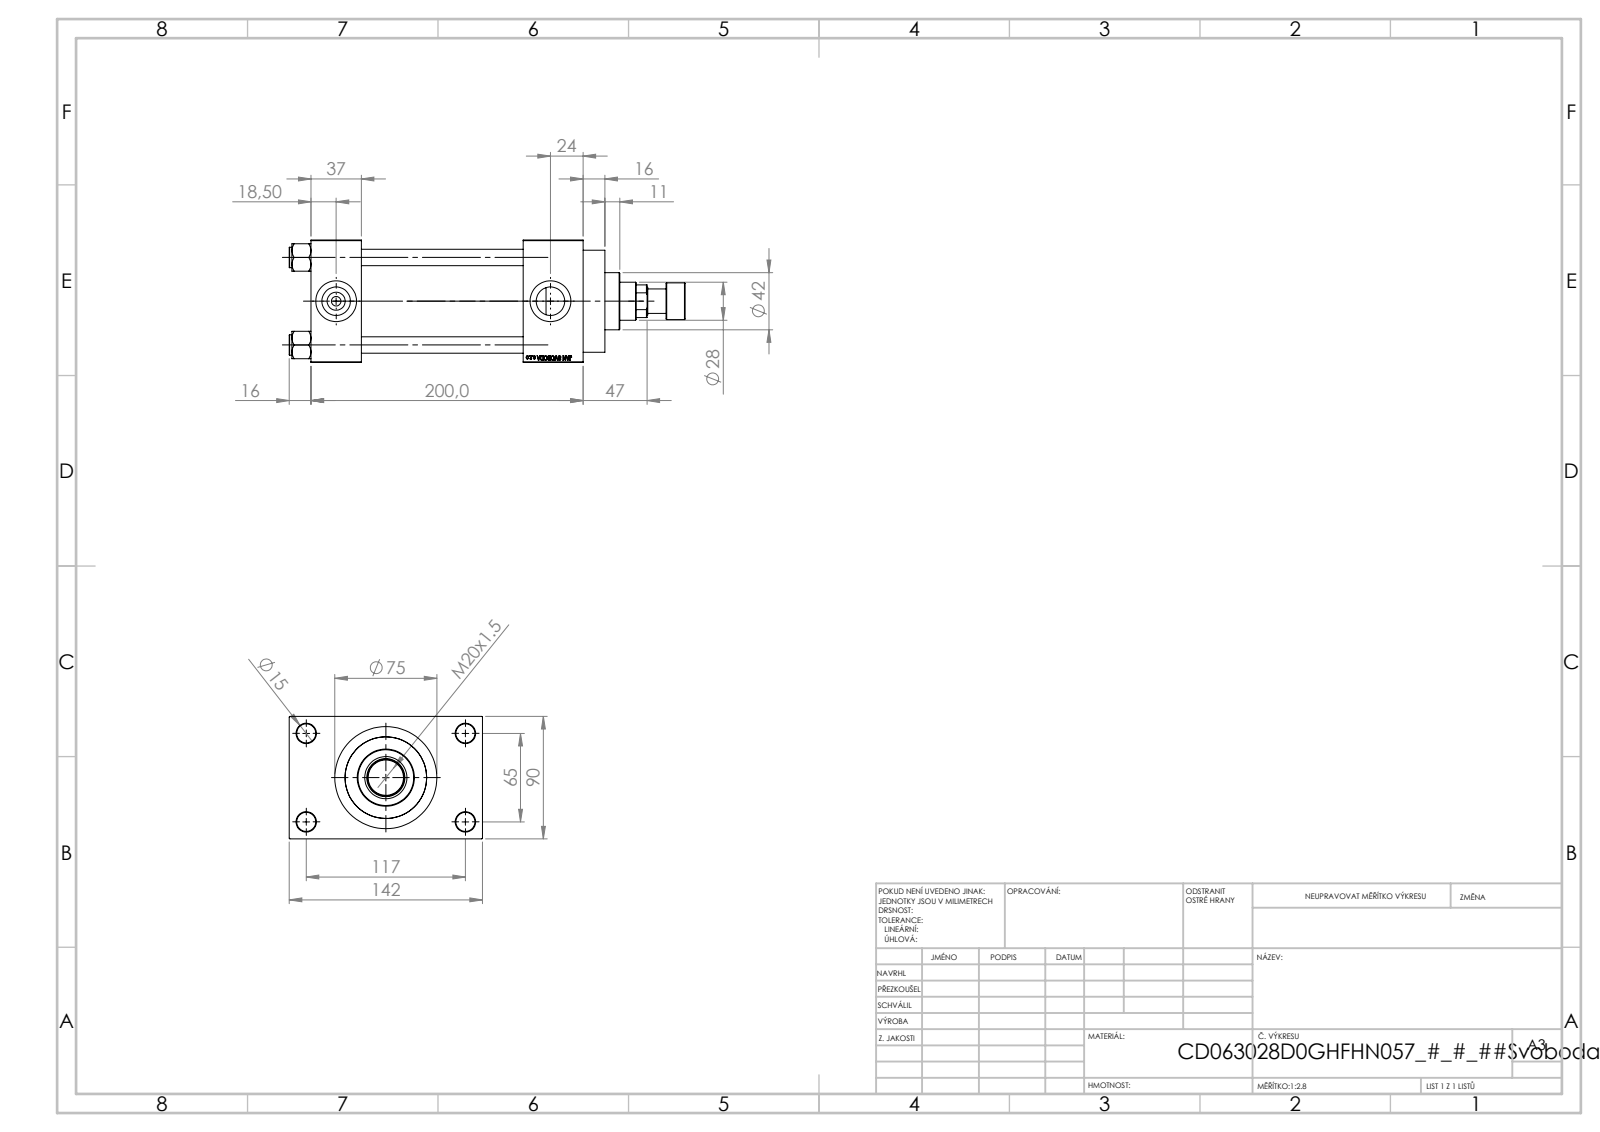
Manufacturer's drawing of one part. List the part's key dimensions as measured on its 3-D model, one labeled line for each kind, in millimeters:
Part name (STEP PRODUCT): V215CR_ROD_END_F; V215CD_VC_A; V215CD_VCP_D; V215CD_D_TYCINKA (+2 more)
STEP written by: SolidWorks 2019 (CONFIG_CONTROL_DESIGN)
Units: millimetres
Bodies: 12 solids, 1117 faces (501 planar, 92 cylindrical, 524 other)
Overall size (bounding box): 291 × 142 × 90
Volume: 1 209 000 mm³ · Surface area: 242 777 mm²
Round holes (diameter × count): ⌀12 ×4, ⌀14 ×4, ⌀7 ×2, ⌀20.96 ×2, ⌀30 ×2, ⌀18.5 ×1, ⌀28 ×1, ⌀31 ×1, ⌀50 ×1, ⌀60 ×1, ⌀63 ×1
Round bosses / shafts (diameter × count): ⌀15 ×4, ⌀75 ×1, ⌀69 ×1, ⌀42 ×1, ⌀27 ×1, ⌀18 ×1
Main face-to-face distances: 90, 119, 37, 156, 163, 200, 44, 26, 116, 16
Hole centre spacings: 26.35, 45.47, 64.3, 66.92, 69.81, 90.65, 111.34, 65
